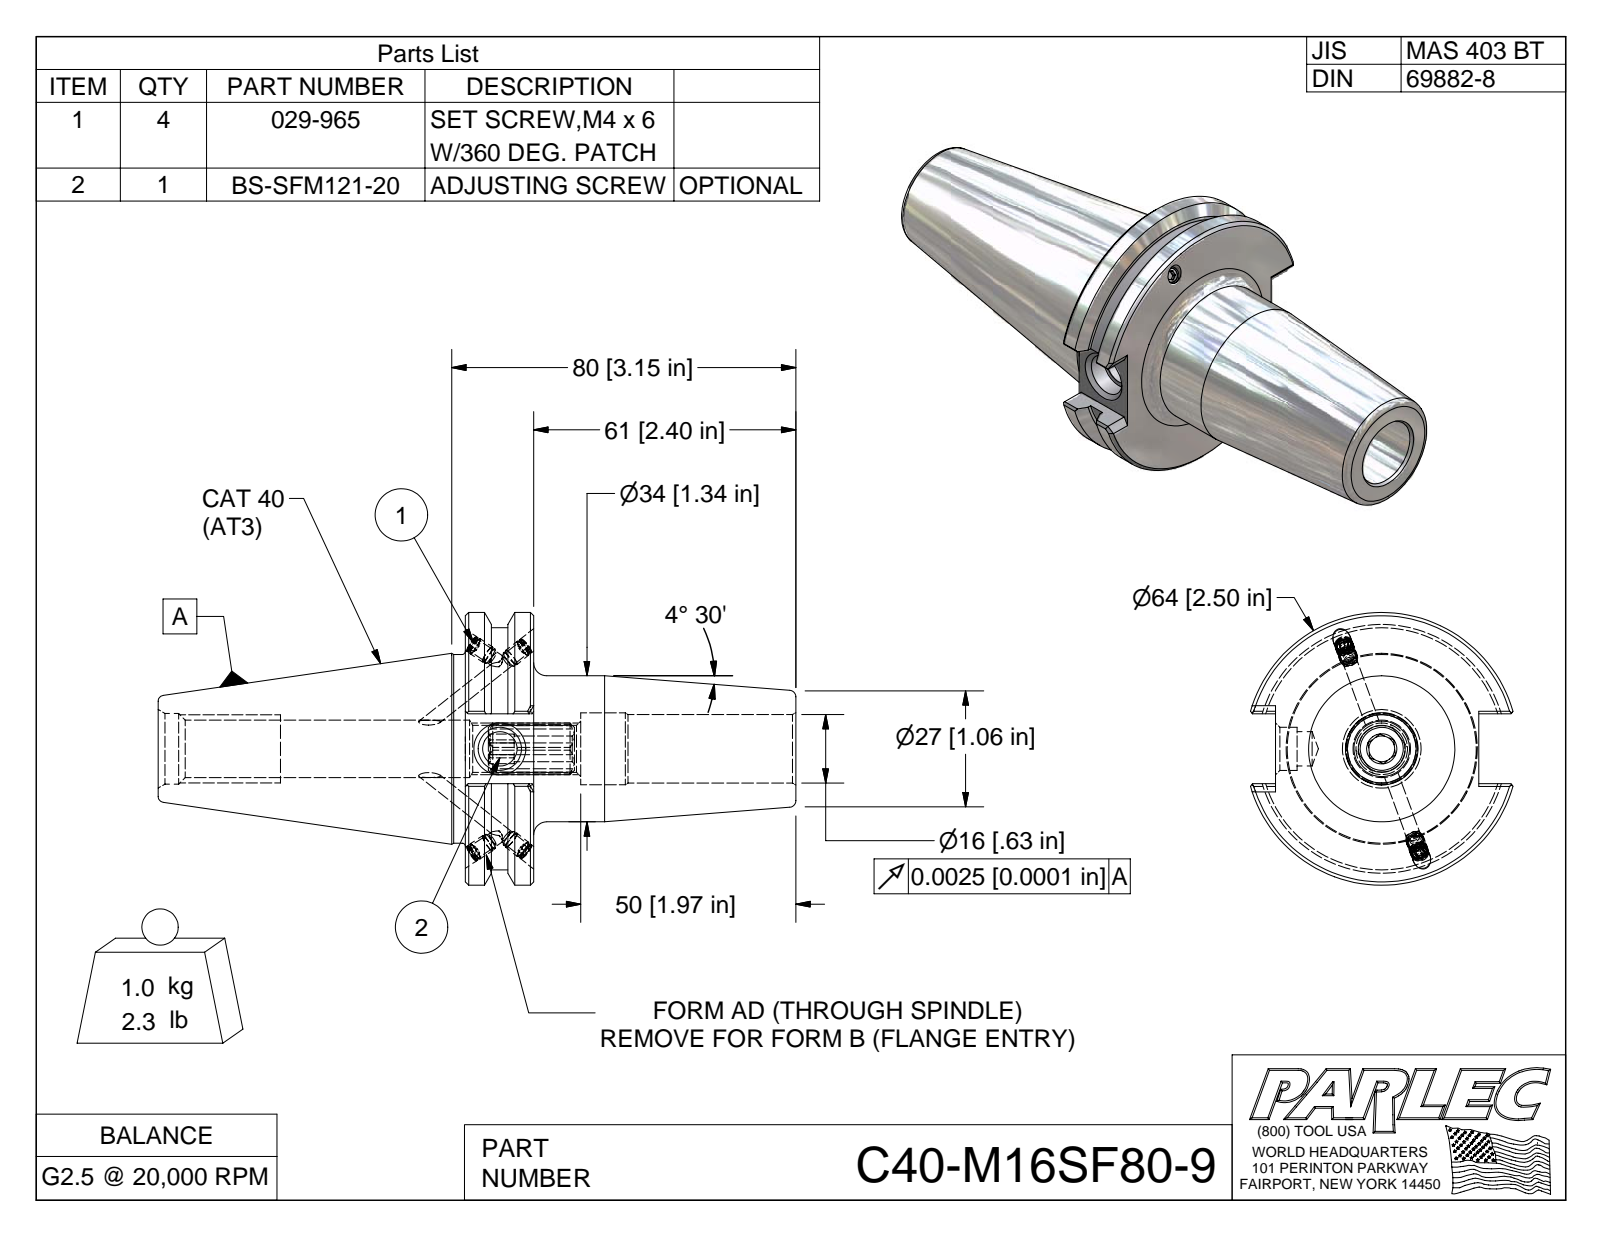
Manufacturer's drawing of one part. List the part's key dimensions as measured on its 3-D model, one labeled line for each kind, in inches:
Part name (STEP PRODUCT): C40-M16SF80-9; C40BC-M16SF80-9-1; 029-965; BS-SFM121-20
STEP written by: Autodesk Inventor 2009 (AUTOMOTIVE_DESIGN)
Units: inches
Bodies: 6 solids, 172 faces (87 planar, 32 cylindrical, 53 other)
Overall size (bounding box): 5.837 × 2.5 × 2.403
Volume: 8.455 in³ · Surface area: 48.08 in²
Round holes (diameter × count): ⌀0.13 ×4, ⌀0.161 ×4, ⌀0.629 ×1, ⌀0.659 ×1
Round bosses / shafts (diameter × count): ⌀0.165 ×4, ⌀0.157 ×4, ⌀2.5 ×1, ⌀2.219 ×1, ⌀1.73 ×1, ⌀1.339 ×1
Partial cylindrical surfaces — rounded edges, fillets, slot ends (radius × count): R0.236 ×1
Main face-to-face distances: 0.625, 3.025, 2.4, 0.64, 0.236, 1.86, 0.394, 2.812, 3.437, 5.837
